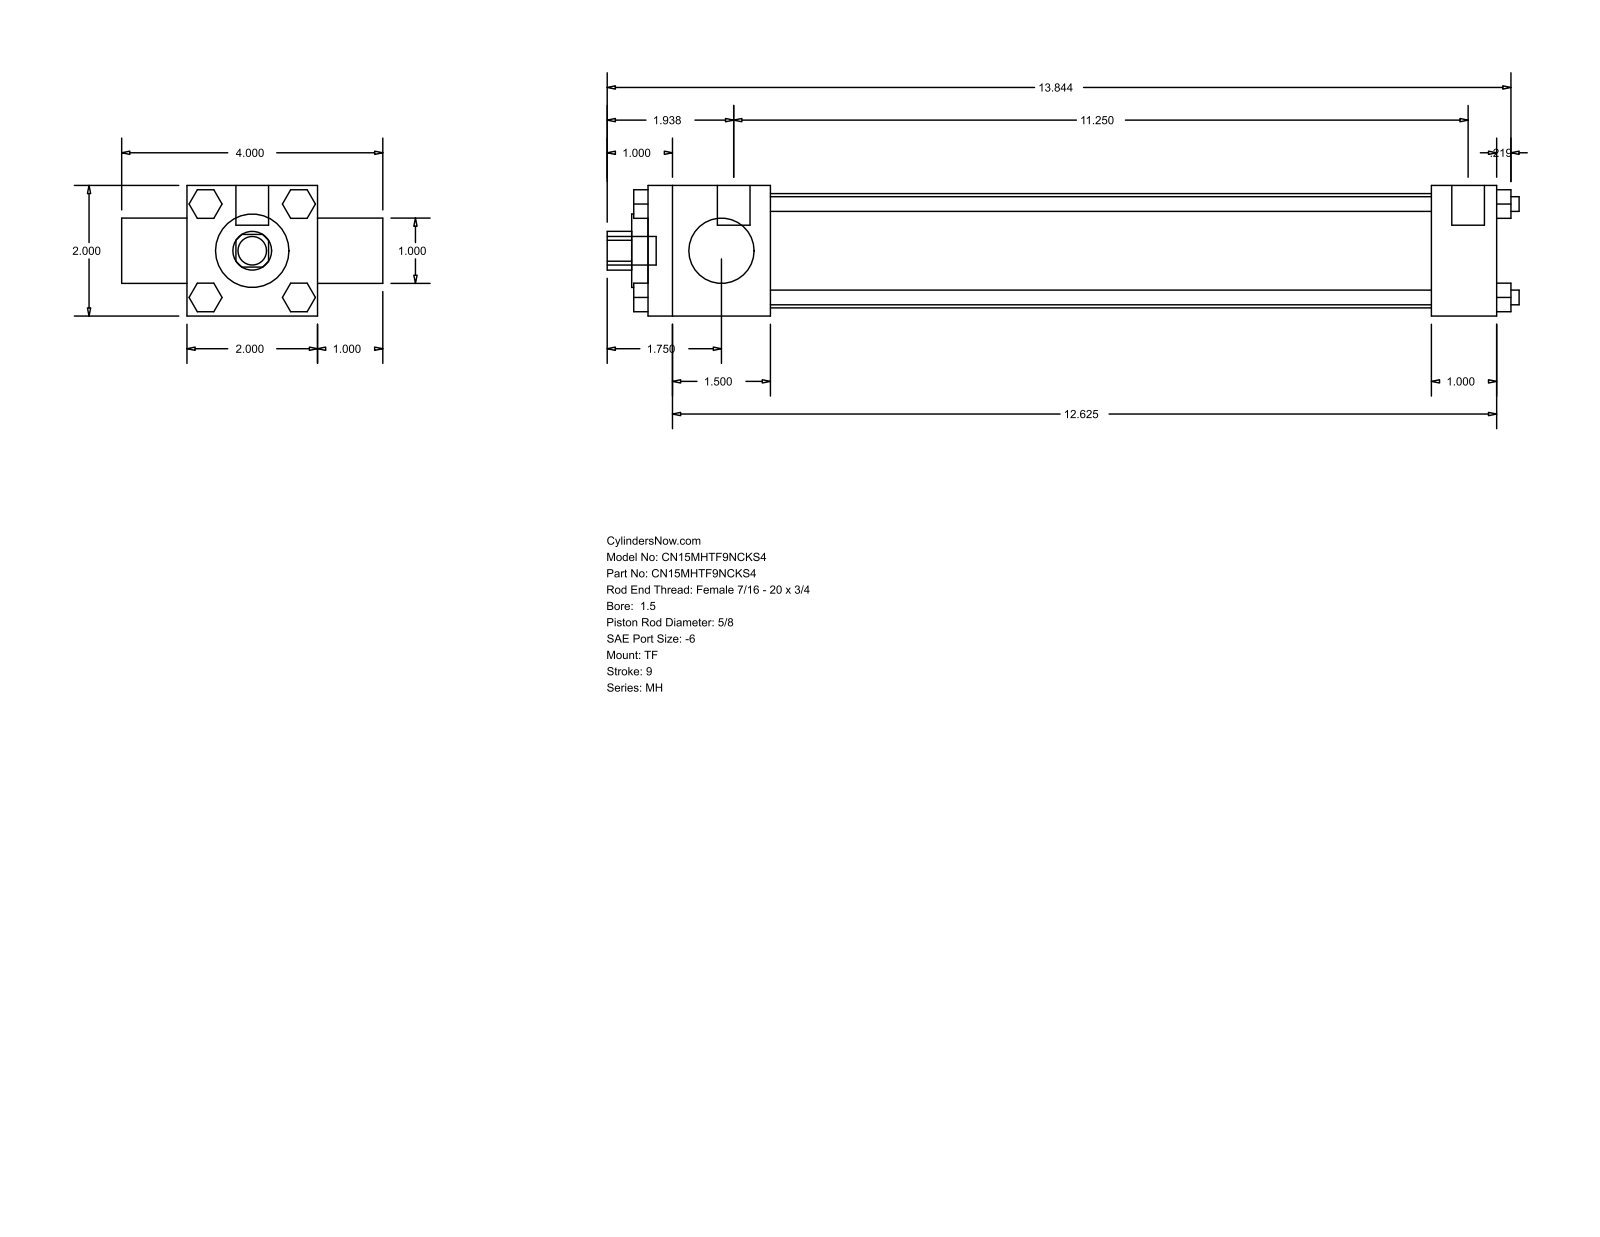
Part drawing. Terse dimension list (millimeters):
name: MH_TF__0150_0.625
written by: GSSL Pune (CONFIG_CONTROL_DESIGN)
unit: mm
bodies: 0 solids, 120 faces (92 planar, 28 cylindrical, 0 other)
size: 354.81 × 101.6 × 50.8
holes: 1× ⌀15.88, 1× ⌀25.4, 1× ⌀28.57, 1× ⌀44.45
bosses: 4× ⌀5.71, 3× ⌀5.56, 2× ⌀12.7, 1× ⌀11.11
rounds: 1× R7.54
face distances: 50.8, 330.19, 25.4, 76.2, 47.62, 282.57, 304.8, 257.18, 25.39, 5.56
